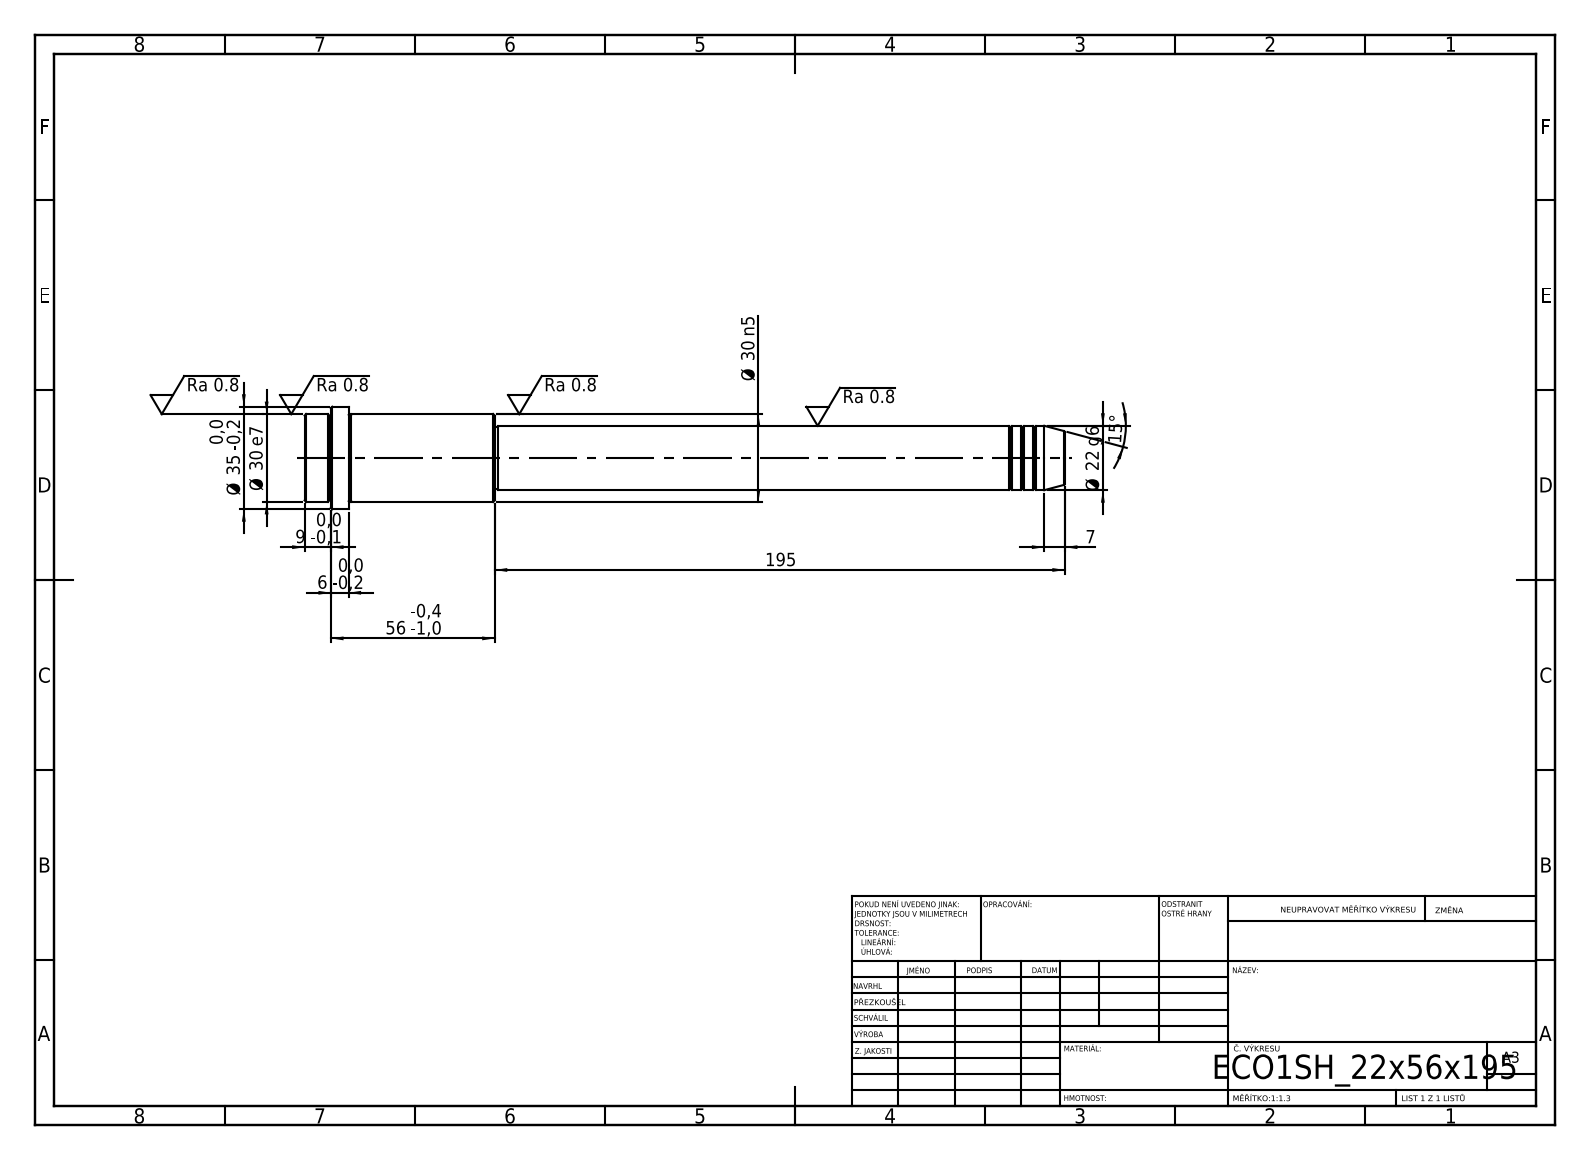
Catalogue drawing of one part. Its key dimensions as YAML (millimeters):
step_written_by: "SolidWorks 2019 (CONFIG_CONTROL_DESIGN)"
units: millimeters
bodies: {solids: 1, faces: 52, planar: 6, cylindrical: 16, other: 30}
overall_size: [260, 35, 35]
volume: 120950
surface_area: 21658
round_bosses_or_shafts:
  - {diameter: 35, count: 1}
  - {diameter: 30, count: 1}
  - {diameter: 22, count: 1}
  - {diameter: 21, count: 1}
face_to_face_distances: [65, 50, 15, 195, 245, 260, 251, 56, 6, 9]
